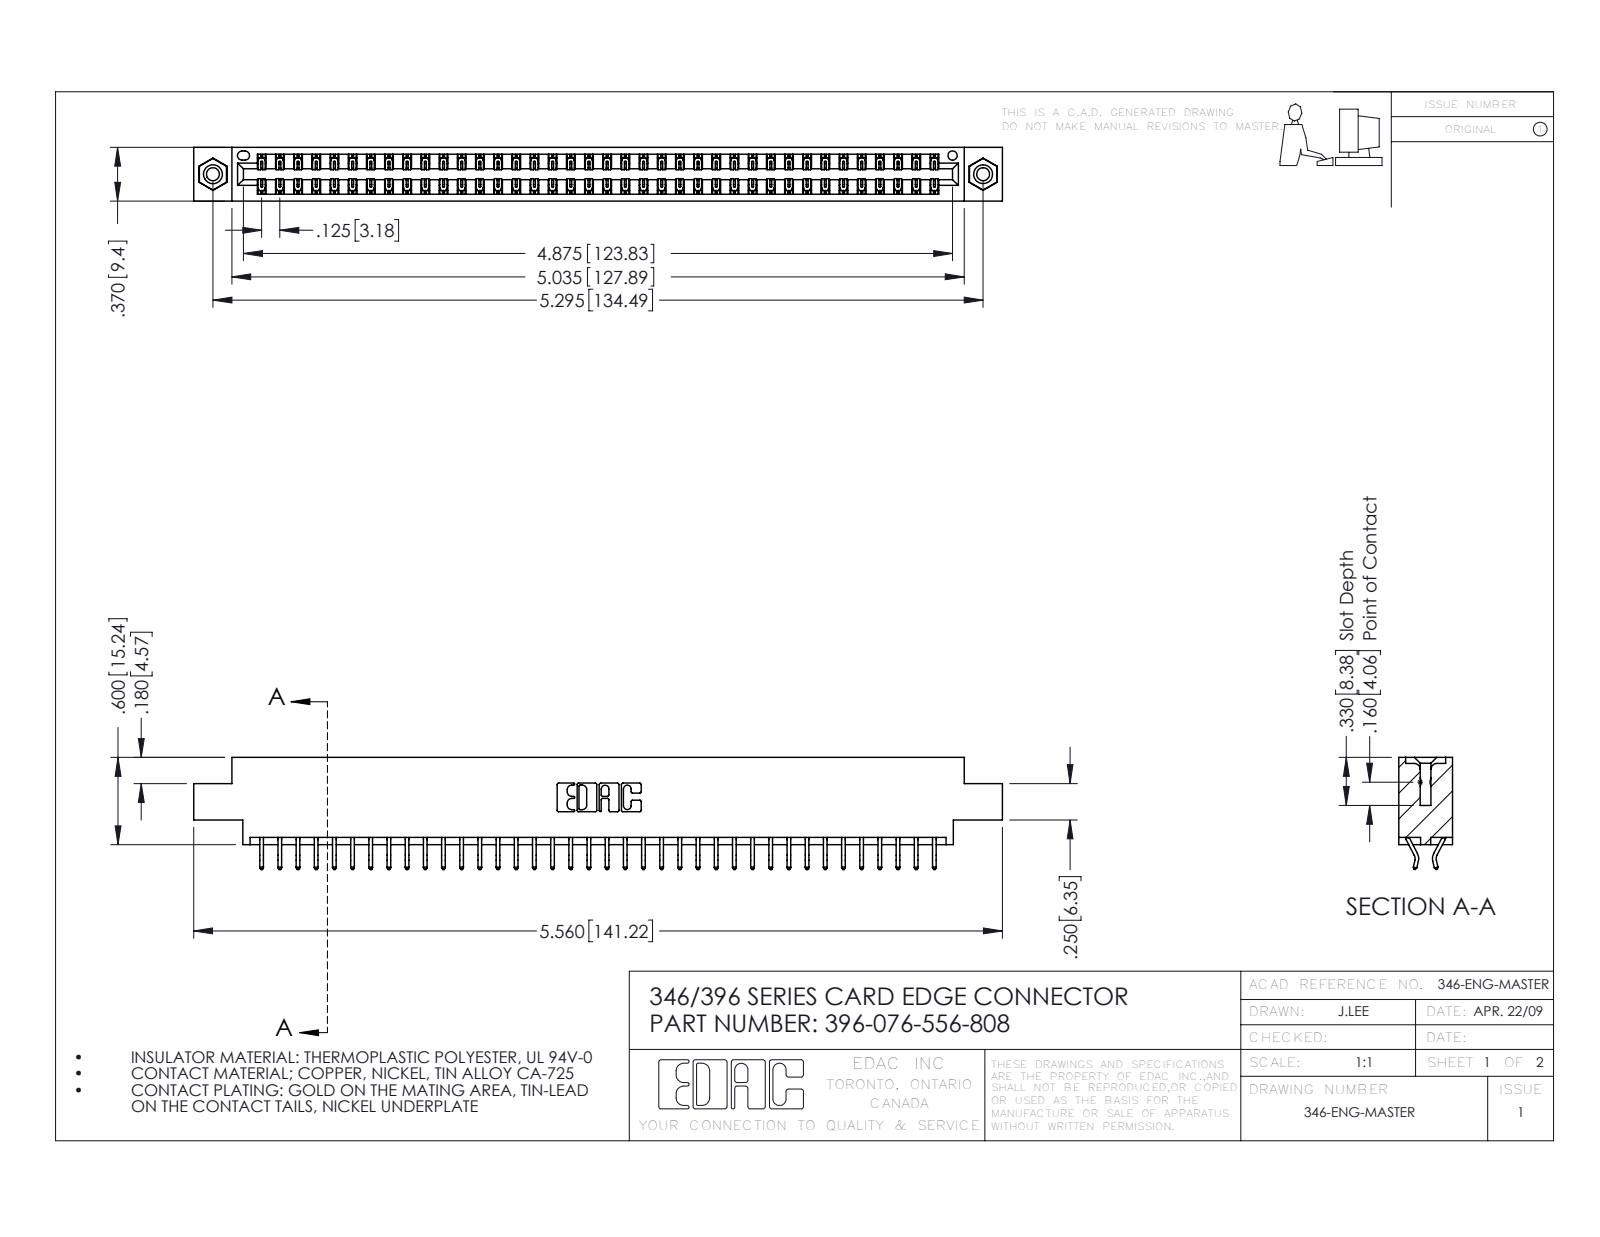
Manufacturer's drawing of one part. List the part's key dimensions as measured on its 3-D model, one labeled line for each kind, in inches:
Part name (STEP PRODUCT): 345-250-001_345-250-003-102; 396-076-556-808; 346 Part_0.170 Offset - 0.156 Dia-TI; 345-292-001_556 Tail
STEP written by: SolidWorks 2016 (CONFIG_CONTROL_DESIGN)
Units: inches
Bodies: 79 solids, 4594 faces (3076 planar, 1502 cylindrical, 16 other)
Overall size (bounding box): 5.56 × 0.77 × 0.37
Volume: 0.828 in³ · Surface area: 29.03 in²
Round holes (diameter × count): ⌀0.089 ×2, ⌀0.125 ×2, ⌀0.156 ×2, ⌀0.064 ×1
Round bosses / shafts (diameter × count): ⌀0.155 ×2
Partial cylindrical surfaces — rounded edges, fillets, slot ends (radius × count): R0.006 ×114, R0.01 ×22, R0.007 ×6, R0.031 ×6, R0.026 ×3, R0.01 ×2, R0.014 ×2, R0.022 ×2
Main face-to-face distances: 0.048, 0.322, 0.37, 0.25, 0.025, 0.072, 0.298, 0.275, 0.222, 0.148
Hole centre spacings: 0.246, 5.086, 5.295
